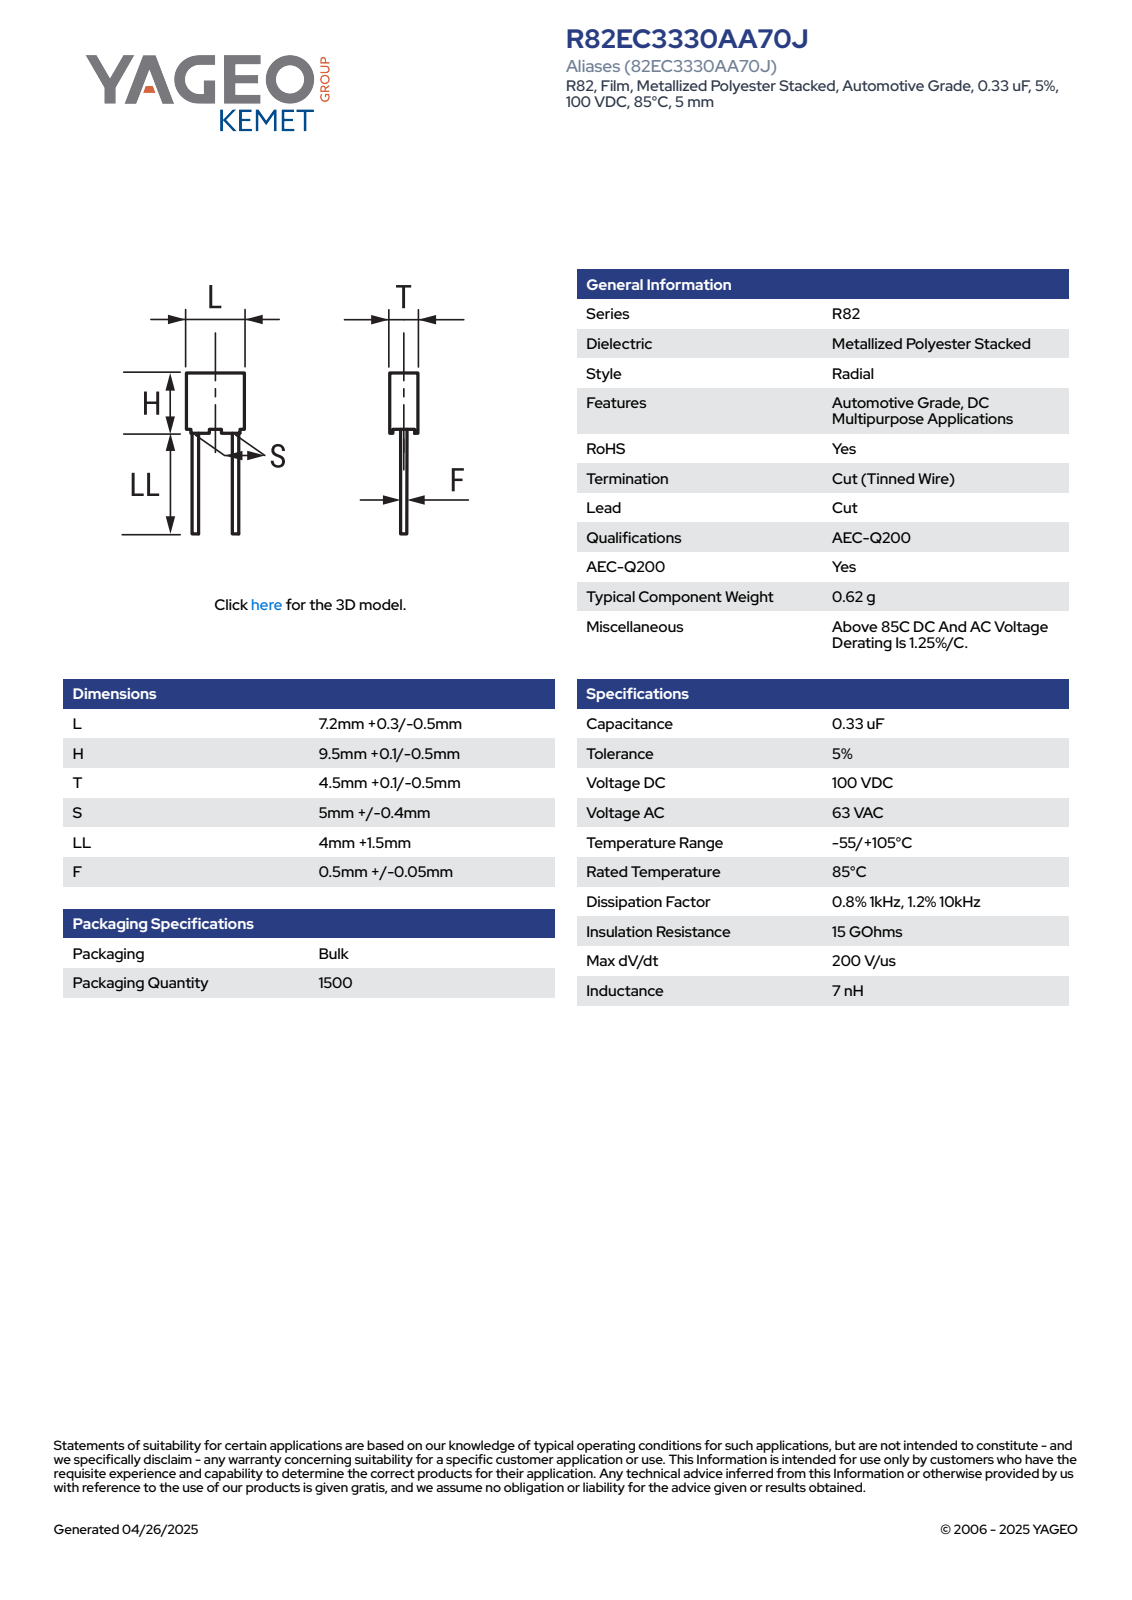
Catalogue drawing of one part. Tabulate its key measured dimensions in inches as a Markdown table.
| quantity | value |
| --- | --- |
| part name | CFR_RB3_7.2X9.5X4.5_L7.5H9.6T4.6S5LL5.5F0.55 |
| STEP written by | SolidWorks 2014 (AUTOMOTIVE_DESIGN) |
| units | inches |
| bodies | 4 solids, 85 faces (77 planar, 8 cylindrical, 0 other) |
| overall size | 0.594 × 0.295 × 0.181 |
| volume | 0.019 in³ |
| surface area | 0.521 in² |
| round bosses / shafts (diameter × count) | 0.022 × 2 |
| partial cylindrical surfaces (radius × count) | 0.02 × 4 |
| main face-to-face distances | 0.181, 0.295, 0.348, 0.171, 0.285, 0.03, 0.378, 0.161, 0.276, 0.013 |
